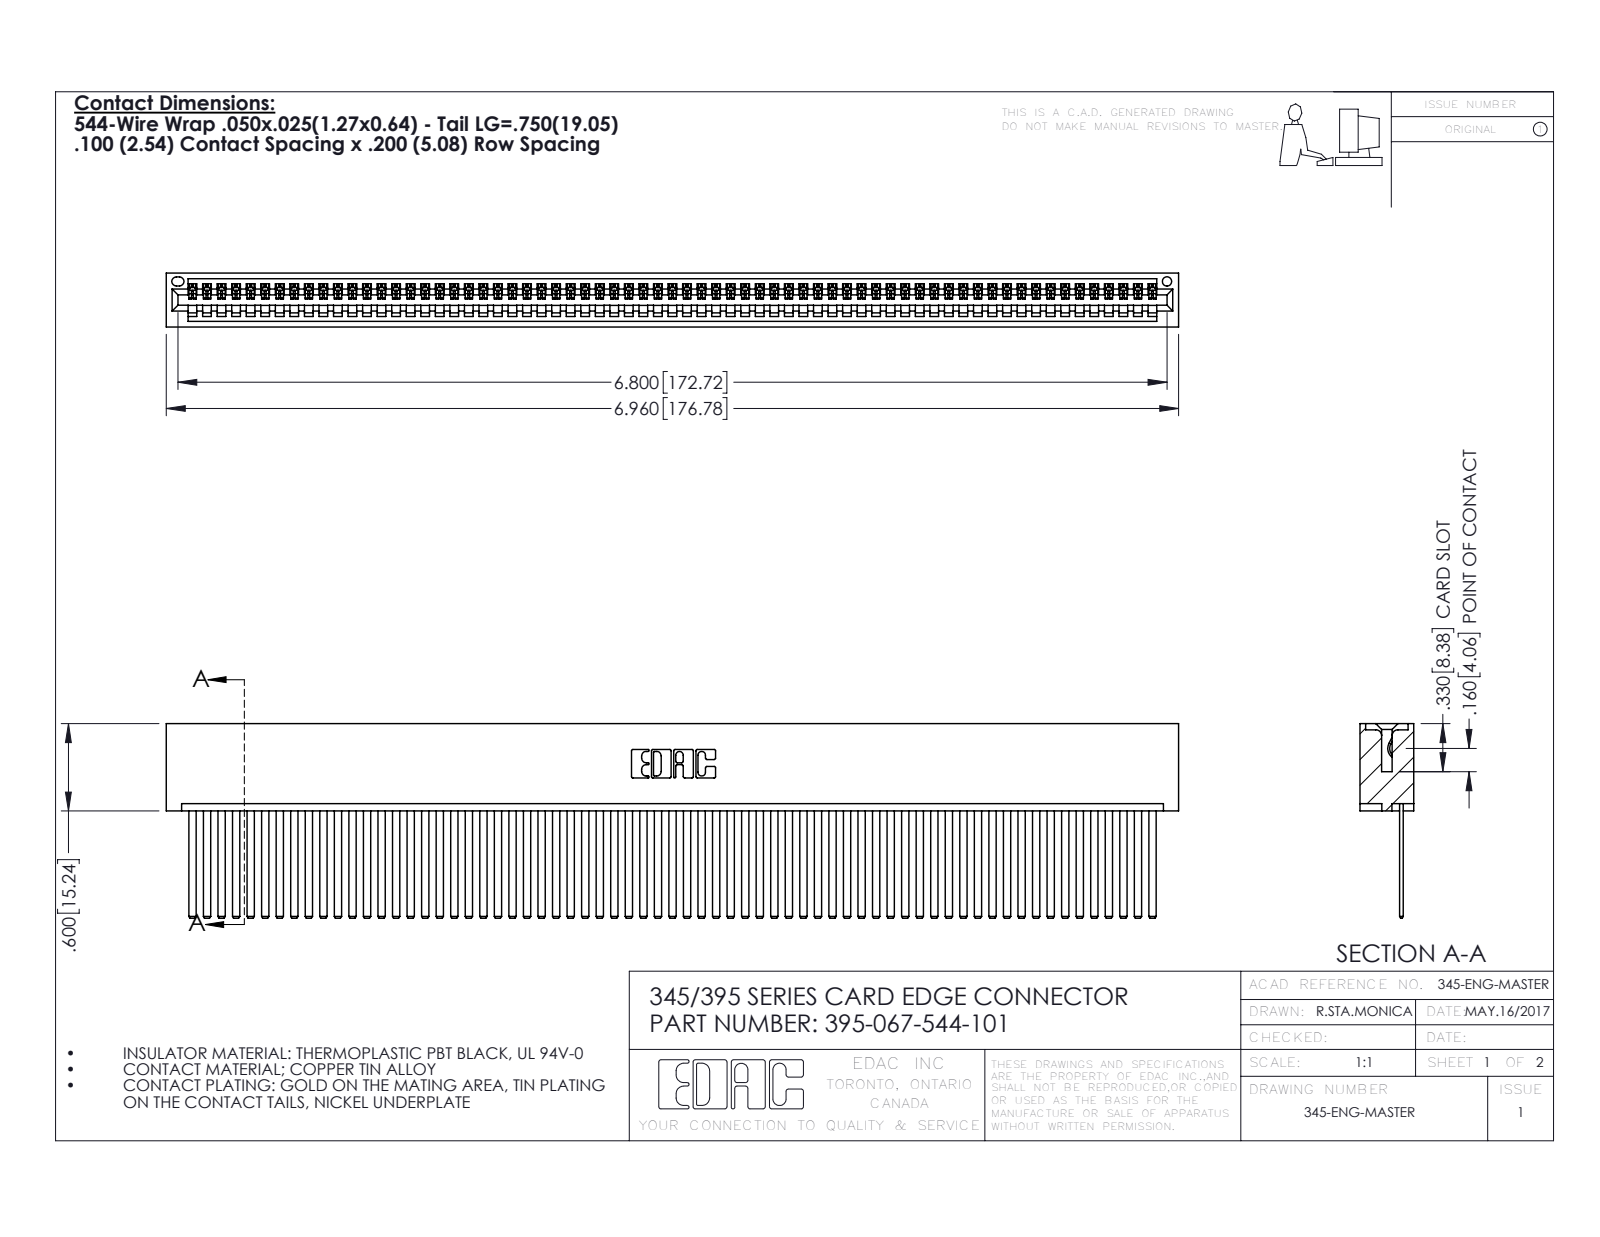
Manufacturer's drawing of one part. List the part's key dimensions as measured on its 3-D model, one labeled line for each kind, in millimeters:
Part name (STEP PRODUCT): 395-067-544-101; 345 Part_No Mounting Lugs; 345-292-001_345-293-144
STEP written by: SolidWorks 2016 (CONFIG_CONTROL_DESIGN)
Units: millimetres
Bodies: 68 solids, 3602 faces (2488 planar, 1114 cylindrical, 0 other)
Overall size (bounding box): 176.8 × 34 × 9.4
Volume: 18 350 mm³ · Surface area: 27 250 mm²
Round holes (diameter × count): ⌀1.6 ×1
Partial cylindrical surfaces — rounded edges, fillets, slot ends (radius × count): R0.2 ×134, R0.3 ×22, R0.2 ×6, R0.8 ×6, R0.7 ×3, R0.8 ×2, R1 ×2, R0.4 ×1
Main face-to-face distances: 1.8, 7.6, 0.6, 2.5, 6.9, 9.4, 5.1, 5.7, 3.8, 1.8
